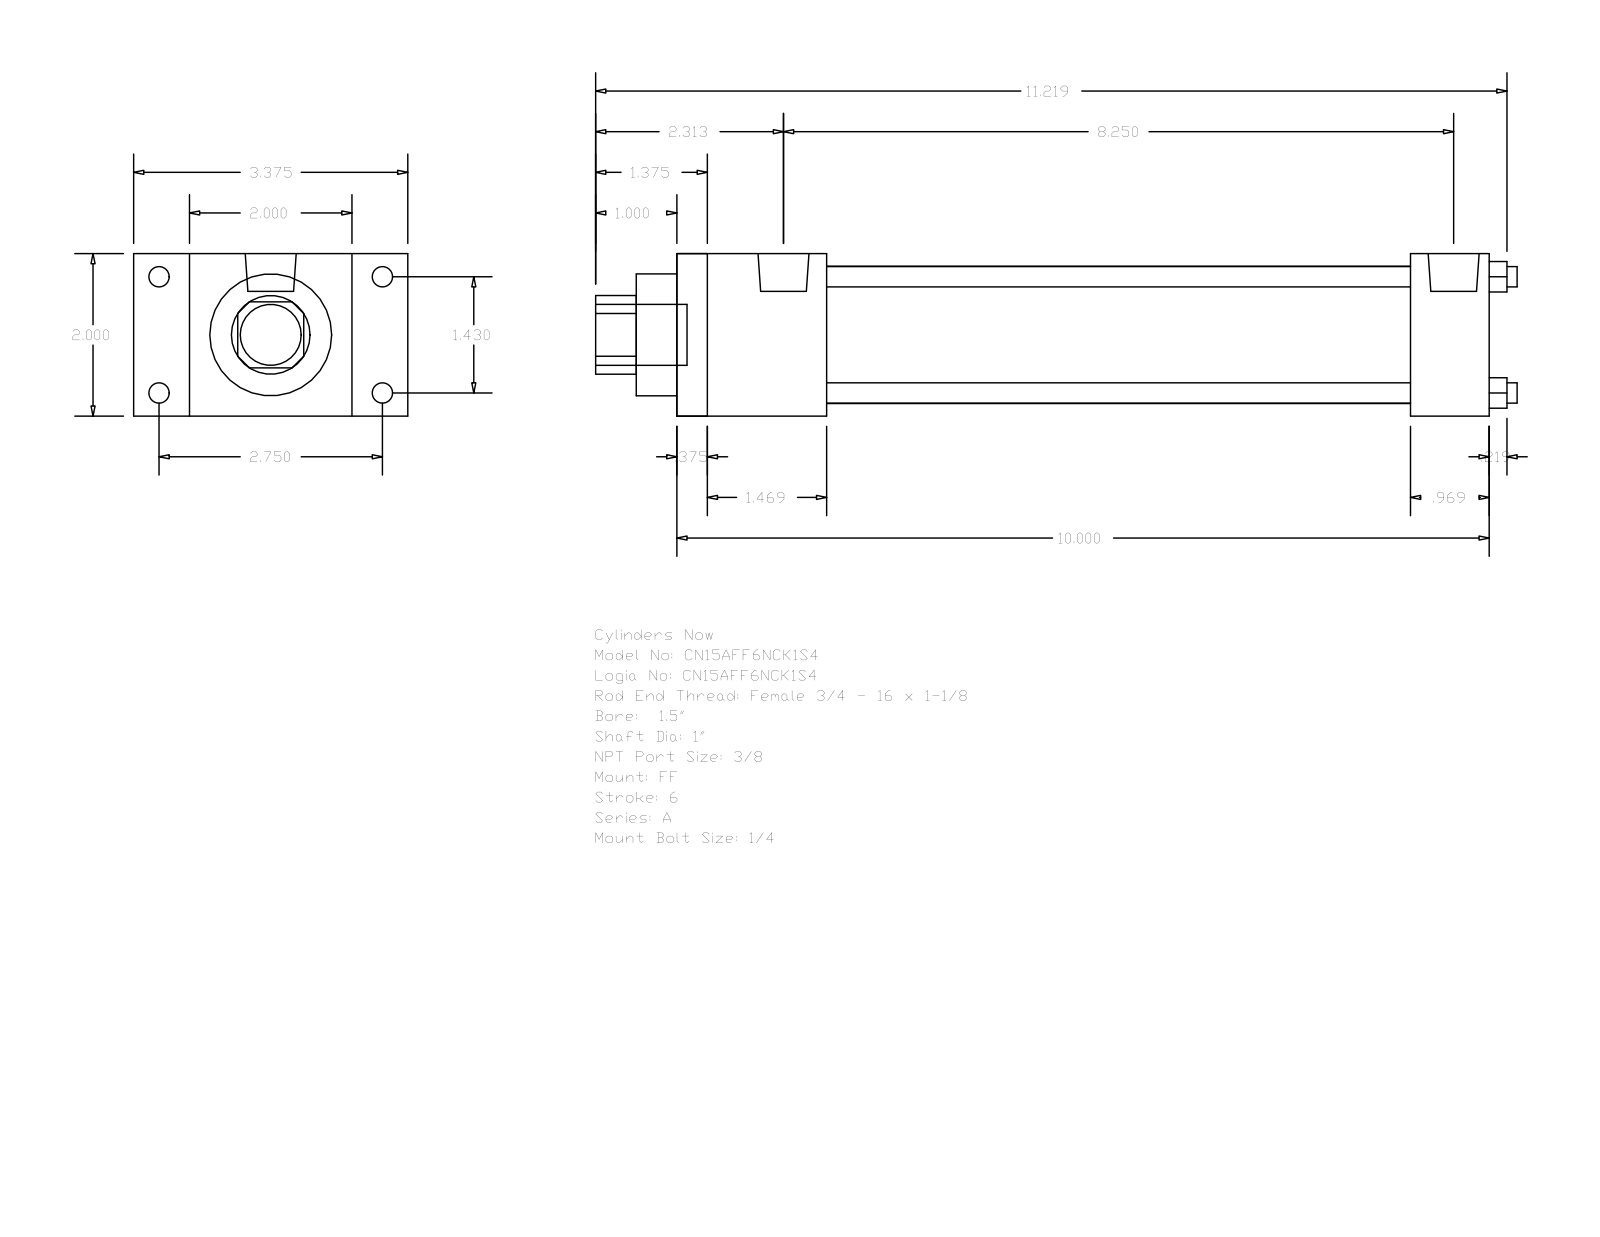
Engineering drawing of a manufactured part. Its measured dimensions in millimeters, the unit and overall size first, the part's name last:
Units: millimetres
Overall size (bounding box): 288.13 × 85.72 × 50.8
Round holes (diameter × count): ⌀6.35 ×4, ⌀25.4 ×1, ⌀38.1 ×1, ⌀42.93 ×1
Round bosses / shafts (diameter × count): ⌀6.35 ×4, ⌀5.56 ×4, ⌀15.93 ×2, ⌀19.05 ×1
Partial cylindrical surfaces — rounded edges, fillets, slot ends (radius × count): R12.29 ×1
Main face-to-face distances: 50.8, 254, 9.52, 244.48, 46.83, 229.39, 37.31, 219.87, 182.56, 207.17
Hole centre spacings: 25.68, 36.32, 51.36
Bodies: 0 solids, 92 faces (64 planar, 28 cylindrical, 0 other)
Part name (STEP PRODUCT): A_FF__0150_1
STEP written by: GSSL Pune (CONFIG_CONTROL_DESIGN)
